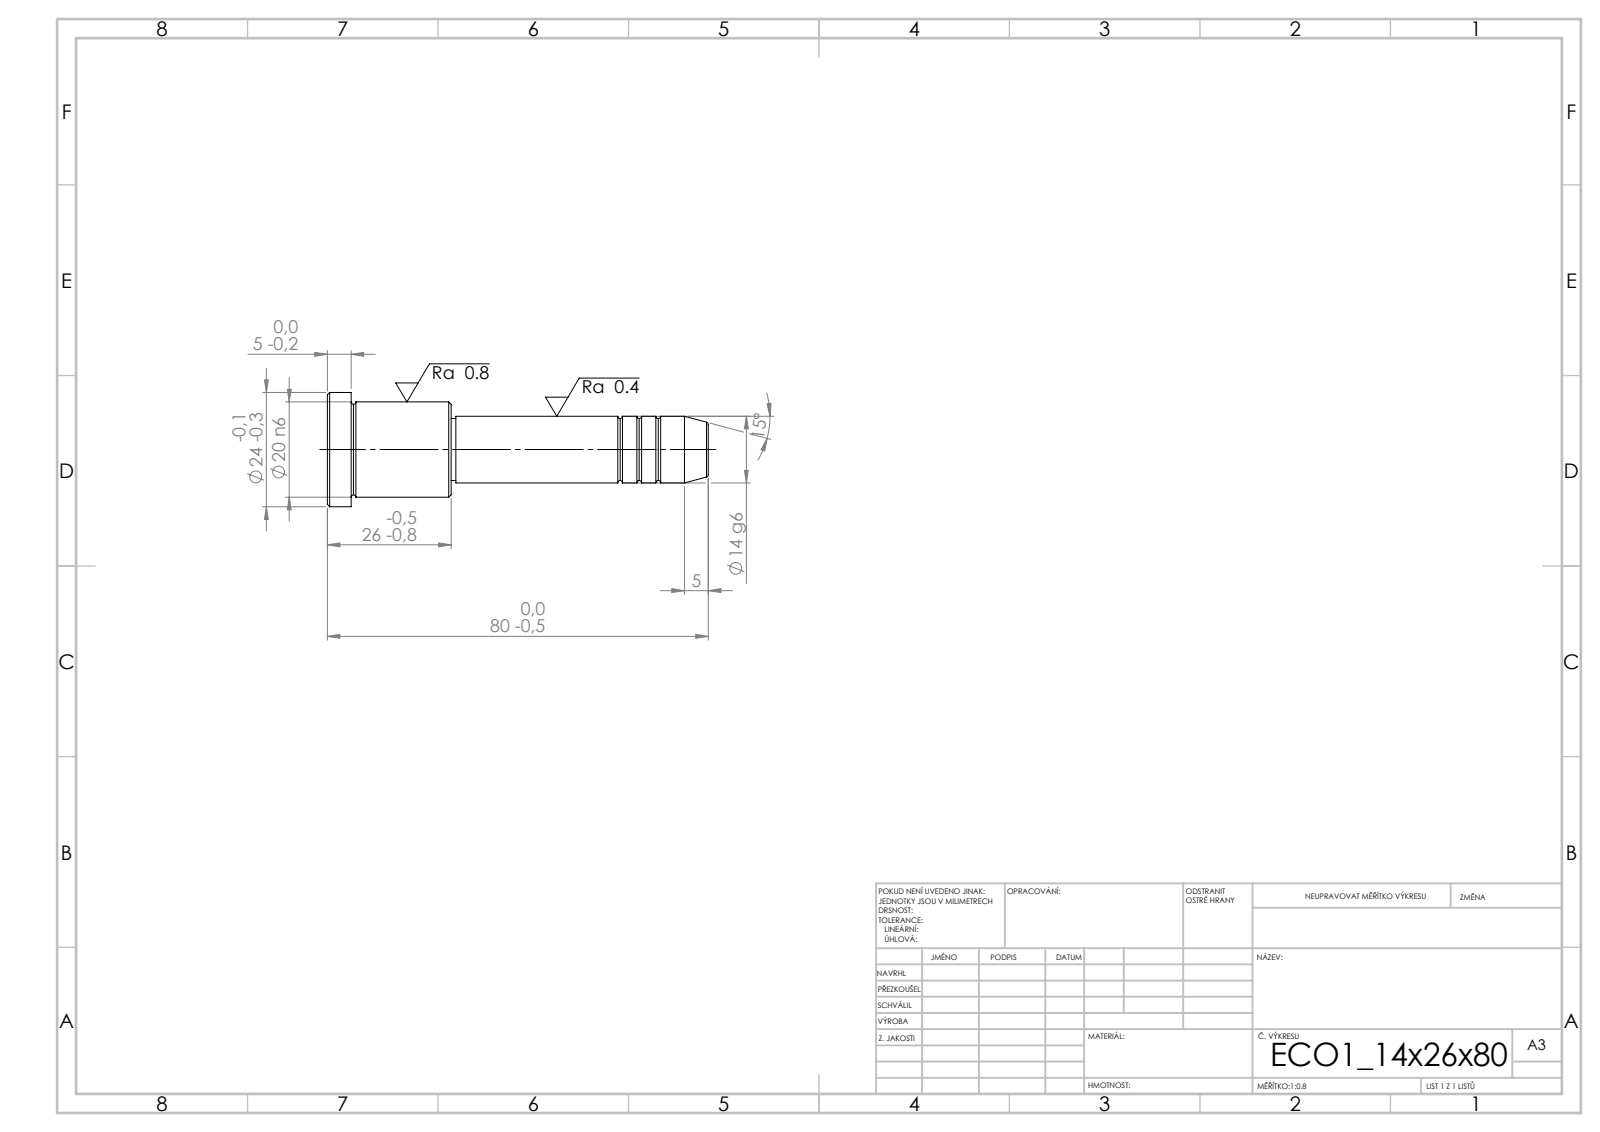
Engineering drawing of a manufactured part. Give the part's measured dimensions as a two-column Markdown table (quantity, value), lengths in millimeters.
| quantity | value |
| --- | --- |
| STEP written by | SolidWorks 2019 (CONFIG_CONTROL_DESIGN) |
| units | millimeters |
| bodies | 1 solid, 43 faces (5 planar, 14 cylindrical, 24 other) |
| overall size | 80 × 24 × 24 |
| volume | 16 920 mm³ |
| surface area | 5 002 mm² |
| round bosses / shafts (diameter × count) | 24 × 1, 20 × 1, 14 × 1, 13 × 1 |
| main face-to-face distances | 26, 21, 5, 54, 75, 80, 53, 1, 22, 27 |
